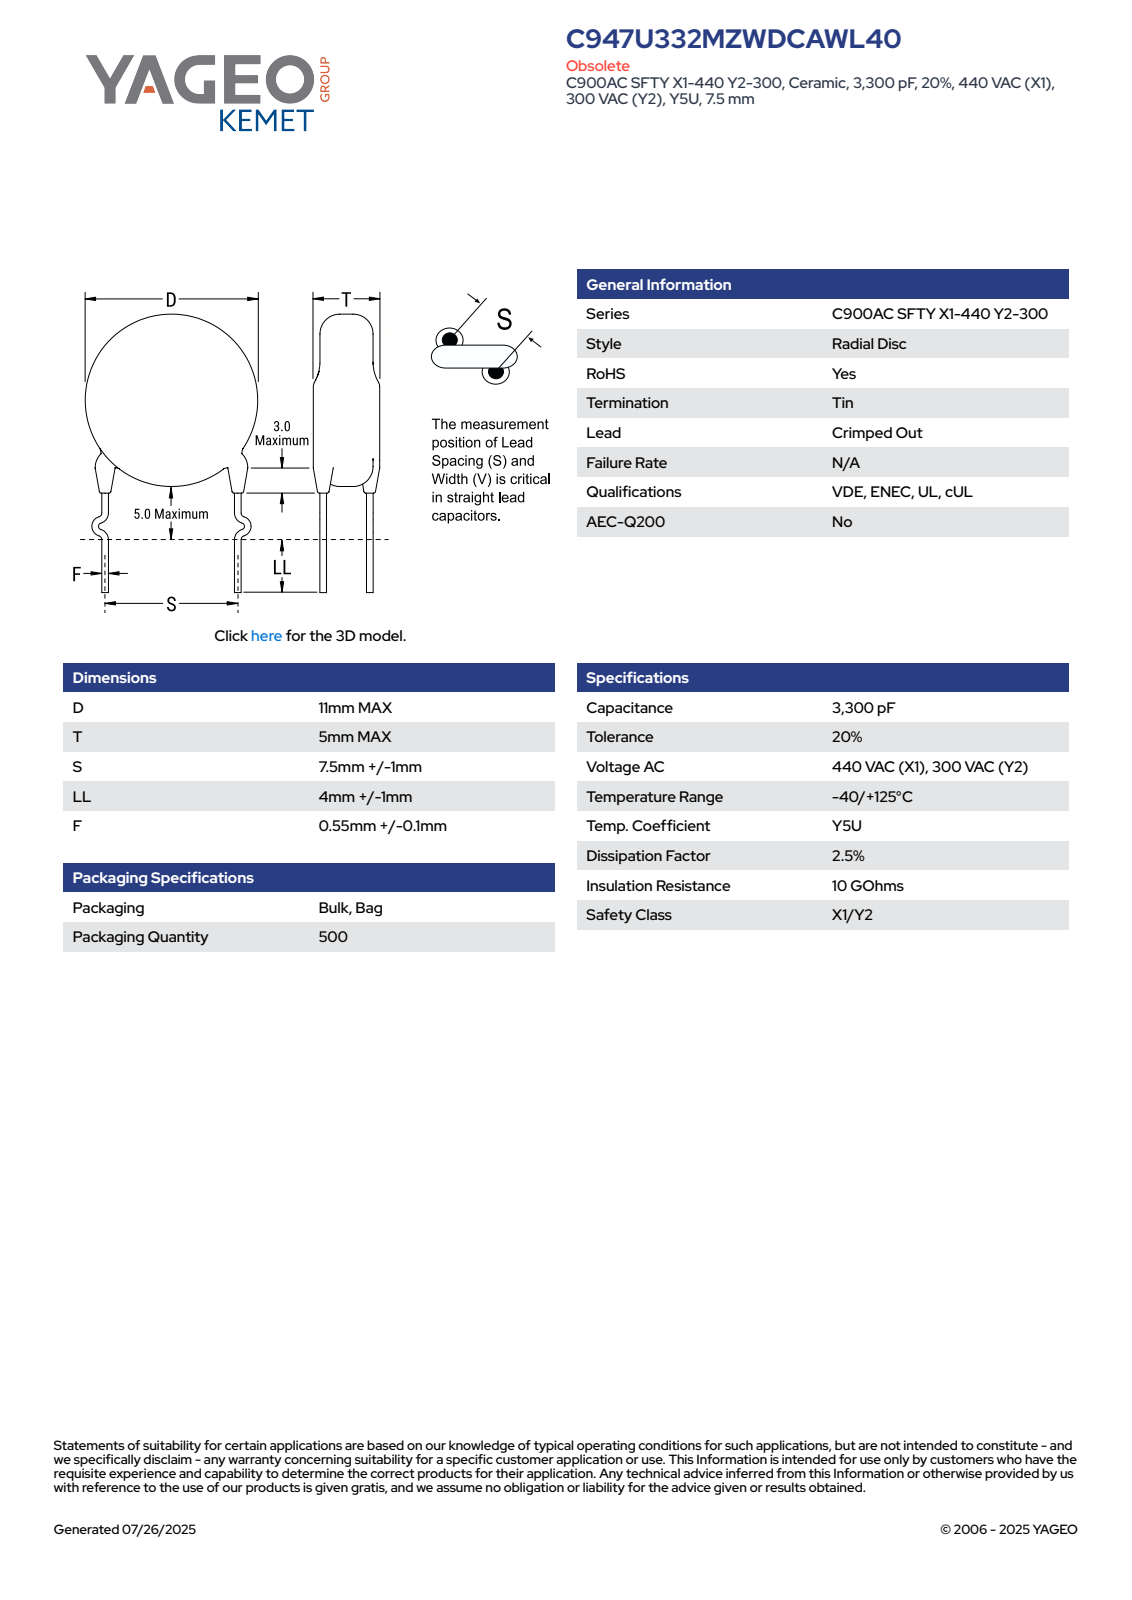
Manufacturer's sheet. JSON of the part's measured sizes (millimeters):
{"part_name": "CCD_KCOC900_D11T5S7.5LL5F0.55", "step_written_by": "SolidWorks 2014 (AUTOMOTIVE_DESIGN)", "units": "millimeters", "bodies": {"solids": 4, "faces": 85, "planar": 63, "cylindrical": 6, "other": 16}, "overall_size": [21, 12.55, 5], "volume_mm3": 472, "surface_area_mm2": 401, "round_bosses_or_shafts": [[1.2, 2], [11, 1]], "face_to_face_distances": [5, 1.14, 6.08, 4.94, 0.32, 0.92, 4.67, 2.36, 3.39, 3.53]}
